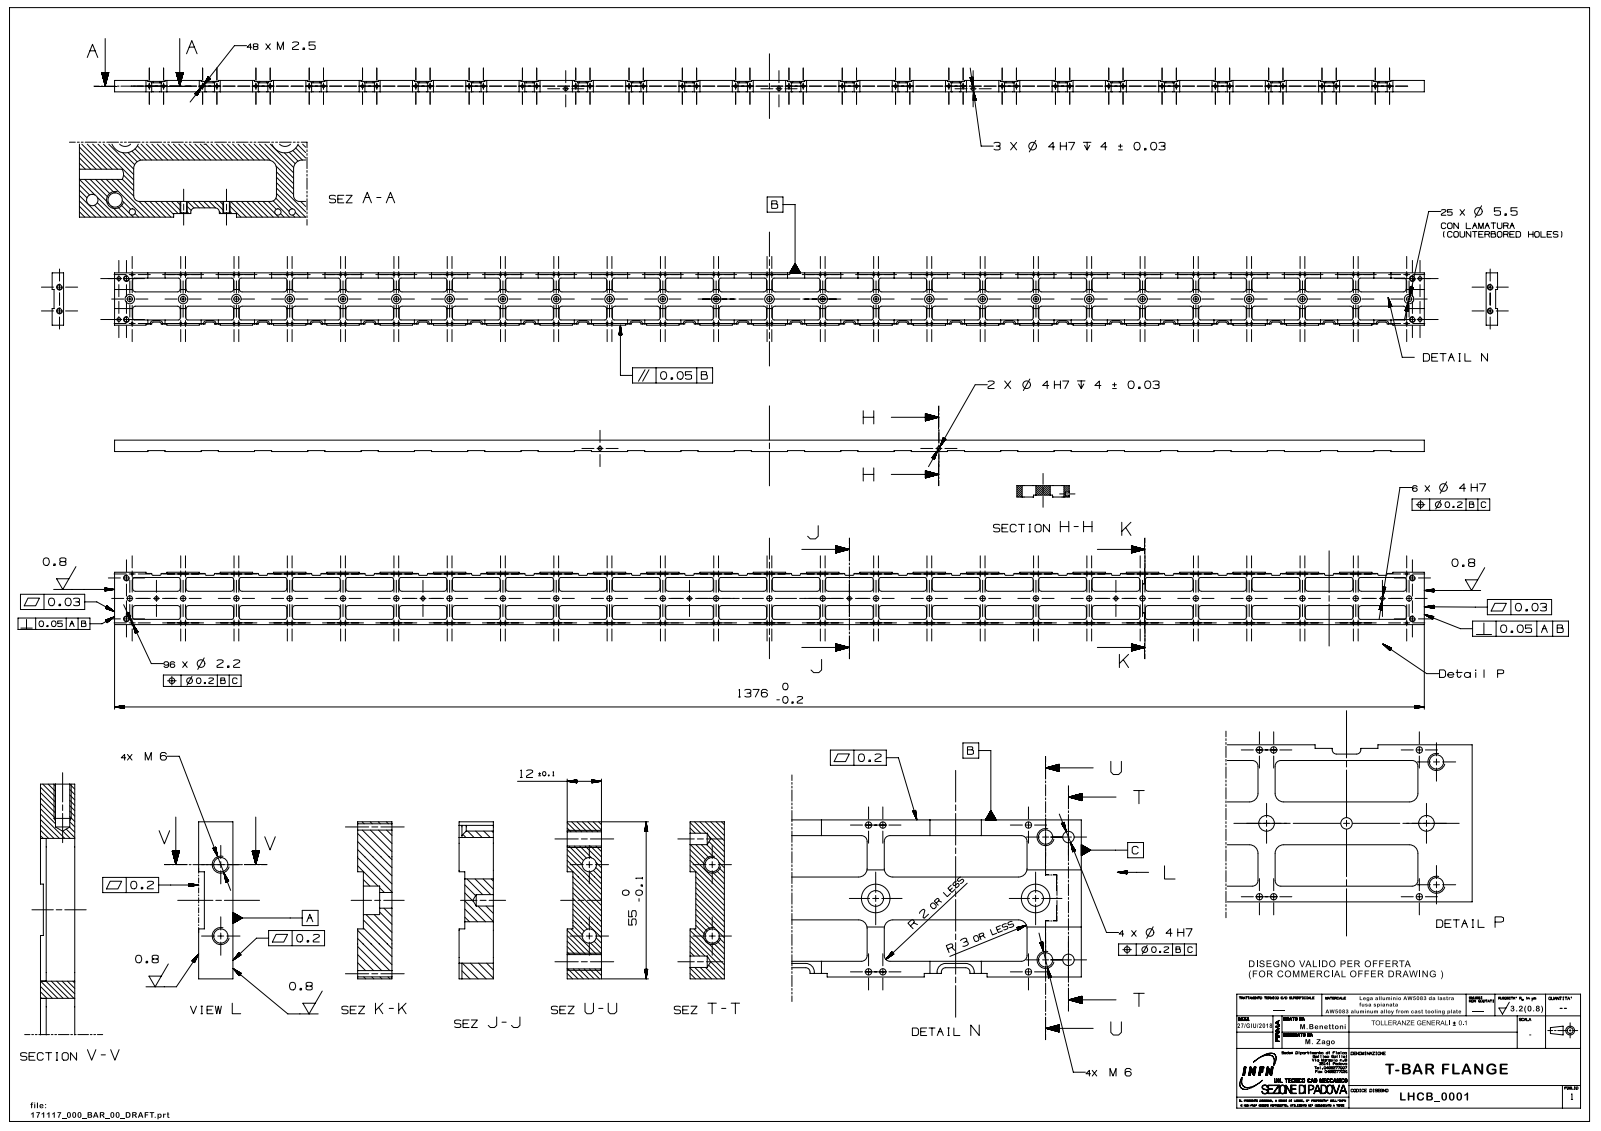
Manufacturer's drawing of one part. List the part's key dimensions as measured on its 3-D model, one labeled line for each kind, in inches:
Part name (STEP PRODUCT): zago1E24C2460ts9
STEP written by: SIEMENS PLM Software NX 11.0 (AP203_CONFIGURATION_CONTROLLED_3D_DESIGN_OF_MECHANICAL_PARTS_AND_ASSEMBLIES_MIM_LF)
Units: inches
Bodies: 1 solid, 1303 faces (736 planar, 457 cylindrical, 110 other)
Overall size (bounding box): 54.173 × 2.165 × 0.472
Volume: 25.07 in³ · Surface area: 306.3 in²
Round holes (diameter × count): ⌀0.087 ×96, ⌀0.081 ×48, ⌀0.217 ×25, ⌀0.394 ×25, ⌀0.157 ×15, ⌀0.197 ×6
Partial cylindrical surfaces — rounded edges, fillets, slot ends (radius × count): R0.079 ×96, R0.118 ×96, R0.059 ×48
Main face-to-face distances: 0.217, 1.949, 0.571, 1.161, 0.787, 1.378, 0.394, 0.079, 0.472, 1.732
Hole centre spacings: 2.205, 4.409, 6.614, 8.819, 11.024, 2.993, 13.228, 4.852
